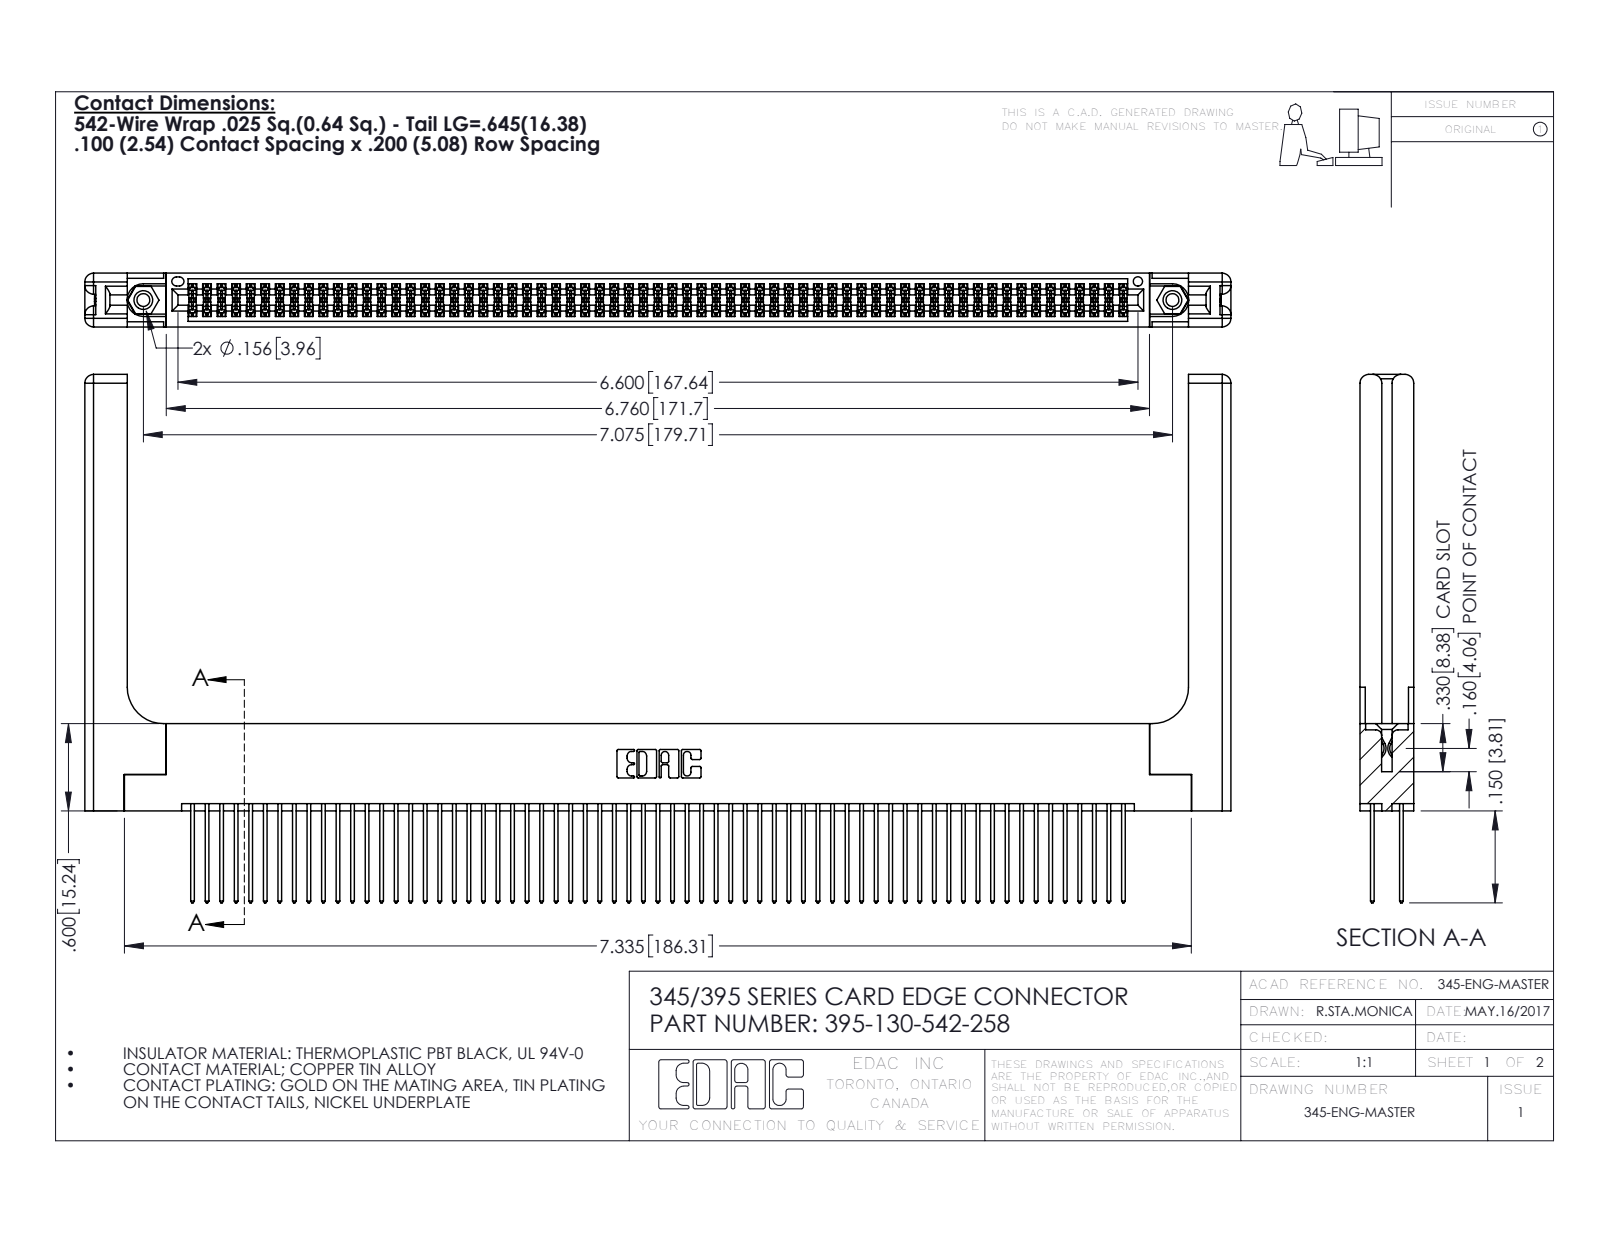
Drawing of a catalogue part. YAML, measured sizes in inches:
part_name: "395-130-542-258; 345-250-001_345-250-001-102; 345 Part_Flush Mounting Lugs - 0.156 Dia-TH; 345-220-058_345-220-058 (+1 more)"
step_written_by: "SolidWorks 2016 (CONFIG_CONTROL_DESIGN)"
units: inches
bodies: {solids: 135, faces: 6882, planar: 4518, cylindrical: 2304, other: 60}
overall_size: [7.879, 3.632, 0.37]
volume: 1.754
surface_area: 59.34
round_holes:
  - {diameter: 0.089, count: 2}
  - {diameter: 0.125, count: 2}
  - {diameter: 0.156, count: 2}
  - {diameter: 0.064, count: 1}
round_bosses_or_shafts:
  - {diameter: 0.155, count: 2}
partial_cylinders:
  - {radius: 0.006, count: 195}
  - {radius: 0.01, count: 130}
  - {radius: 0.01, count: 22}
  - {radius: 0.06, count: 16}
  - {radius: 0.007, count: 6}
  - {radius: 0.031, count: 6}
  - {radius: 0.026, count: 3}
  - {radius: 0.014, count: 2}
face_to_face_distances: [0.072, 0.298, 0.2, 0.098, 0.272, 0.025, 0.37, 0.225, 0.175, 0.148]
hole_center_spacings: [0.27, 6.839, 7.075]
